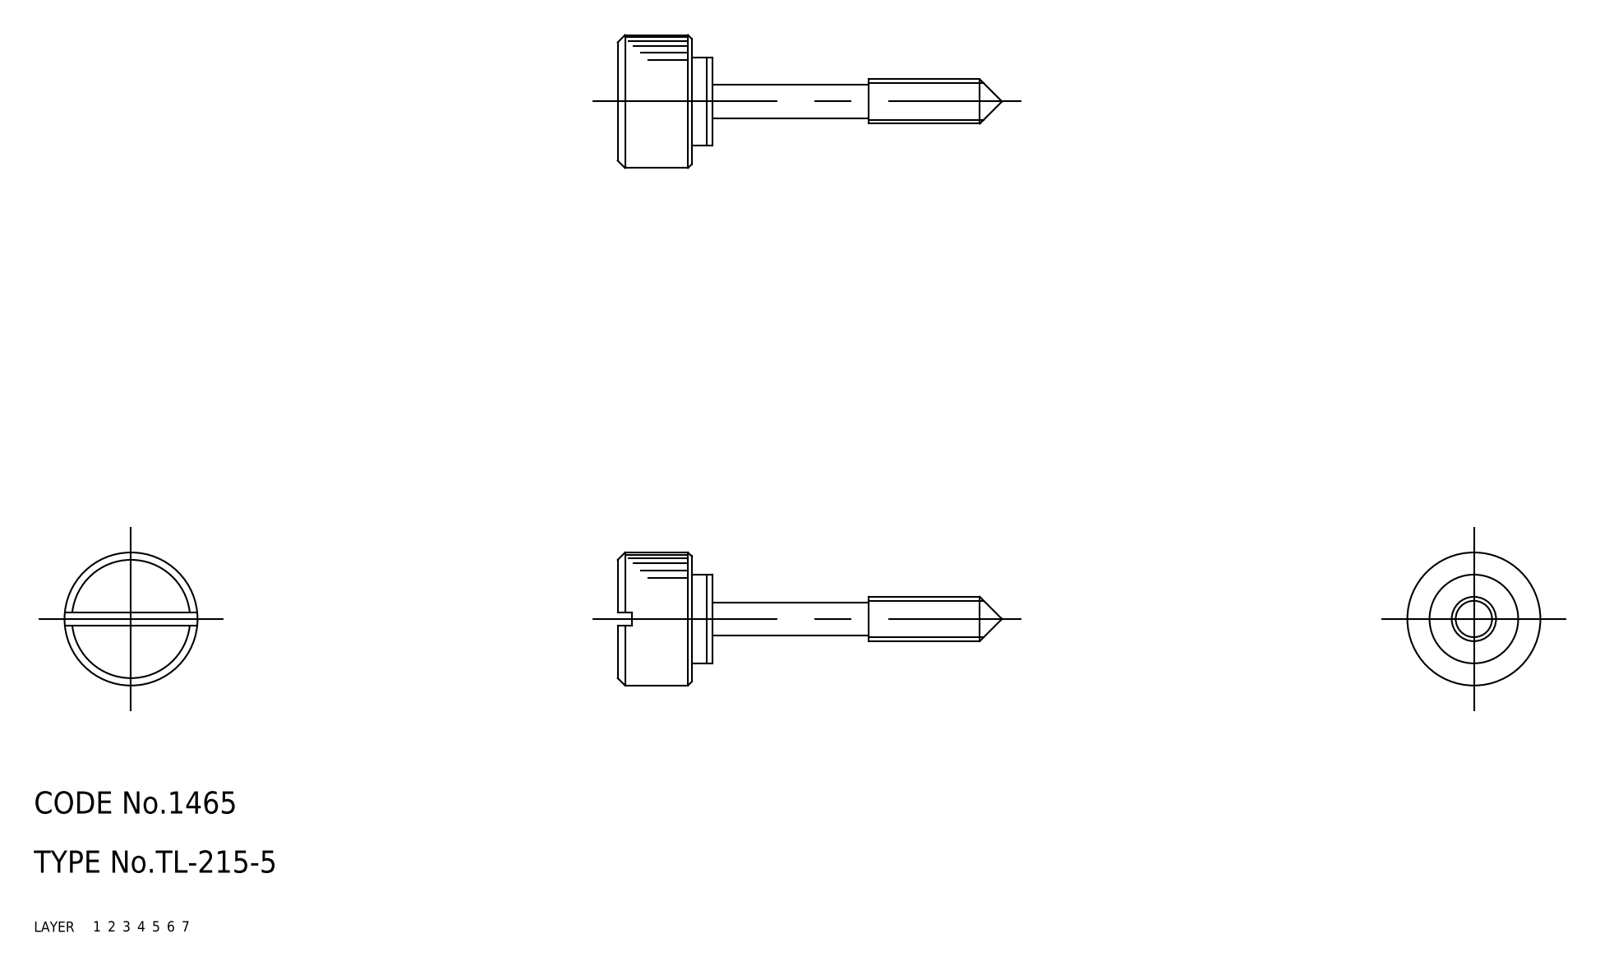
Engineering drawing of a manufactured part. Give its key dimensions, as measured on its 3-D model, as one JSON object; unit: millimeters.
{"part_name": "washer; knob; TL_215_5_25962_36", "step_written_by": "CADfix (AUTOMOTIVE_DESIGN)", "units": "millimeters", "bodies": {"solids": 2, "faces": 42, "planar": 0, "cylindrical": 0, "other": 42}, "overall_size": [52, 18, 18], "volume_mm3": 3557, "surface_area_mm2": 2010}
